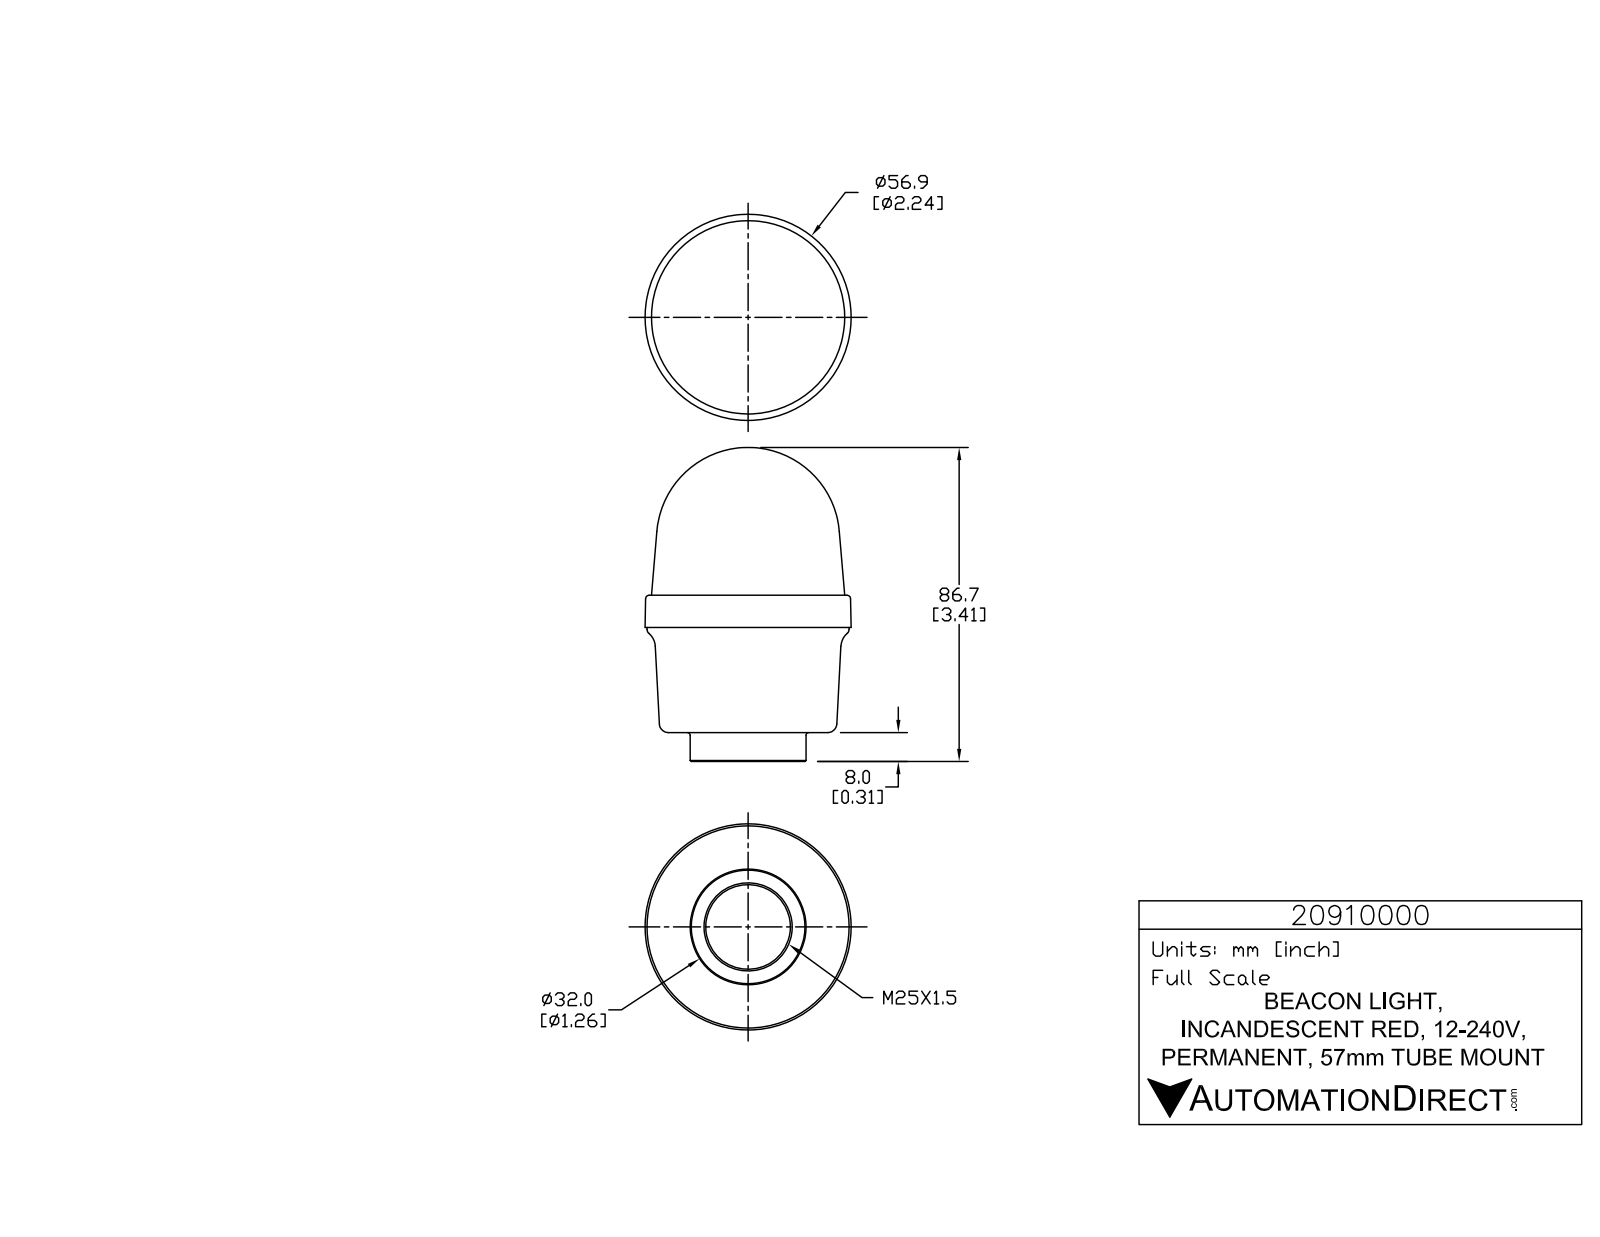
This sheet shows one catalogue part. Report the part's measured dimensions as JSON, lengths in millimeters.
{"part_name": "20910000", "step_written_by": "SolidWorks 2015 (AUTOMOTIVE_DESIGN)", "units": "millimeters", "bodies": {"solids": 1, "faces": 787, "planar": 524, "cylindrical": 168, "other": 95}, "overall_size": [86.7, 56.9, 56.9], "volume_mm3": 150600, "surface_area_mm2": 16310, "round_holes": [[1, 3], [23.4, 1]], "round_bosses_or_shafts": [[5.7, 3], [1.4, 3], [55.8, 1], [32, 1]], "partial_cylinders_radius": [[0.2, 6], [0.2, 6], [0.2, 6], [3.3, 6], [0.1, 3], [0.1, 3], [0.2, 3], [0.2, 3]], "face_to_face_distances": [8, 37.9, 45.9, 8.9, 29, 37, 17.7, 8.8, 46.7, 54.7]}
